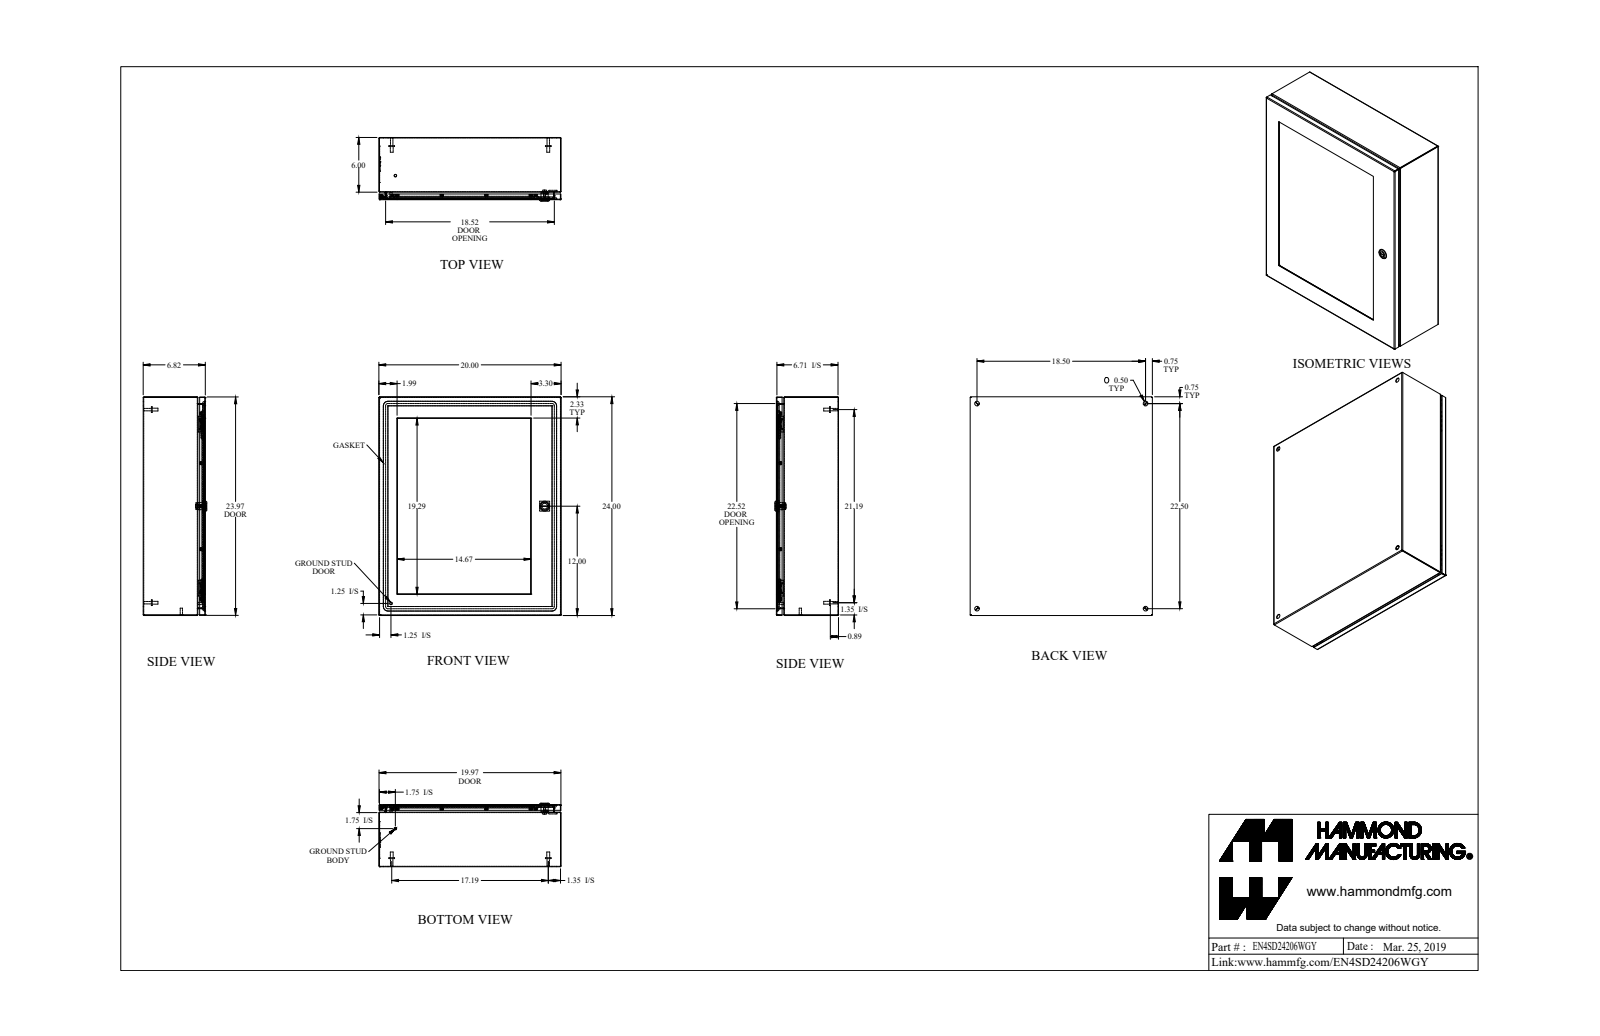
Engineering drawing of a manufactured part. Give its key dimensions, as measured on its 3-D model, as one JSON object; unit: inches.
{"part_name": "EN4SD24206WGY_Default", "step_written_by": "SolidWorks 2019 (CONFIG_CONTROL_DESIGN)", "units": "inches", "bodies": {"solids": 66, "faces": 1333, "planar": 662, "cylindrical": 409, "other": 262}, "overall_size": [24, 20, 6.982], "volume_in3": 168.9, "surface_area_in2": 3796, "round_holes": [[0.13, 18], [0.25, 18], [0.5, 4], [0.172, 1], [0.232, 1], [0.24, 1], [0.242, 1], [0.625, 1], [0.785, 1]], "round_bosses_or_shafts": [[0.226, 19], [0.368, 18], [0.164, 18], [0.625, 4], [0.313, 4], [0.27, 4], [0.281, 2], [0.25, 2]], "partial_cylinders_radius": [[0.029, 21], [0.086, 21], [0.25, 16], [0.125, 10], [19, 8], [0.006, 4], [0.016, 4], [0.062, 4]], "face_to_face_distances": [0.057, 6.765, 6.708, 0.25, 6.458, 6.515, 19.943, 23.943, 0.307, 6.822], "hole_center_spacings": [4.719, 4.89, 4.891, 9.78, 10.324, 16.401, 18.324, 20.333]}
